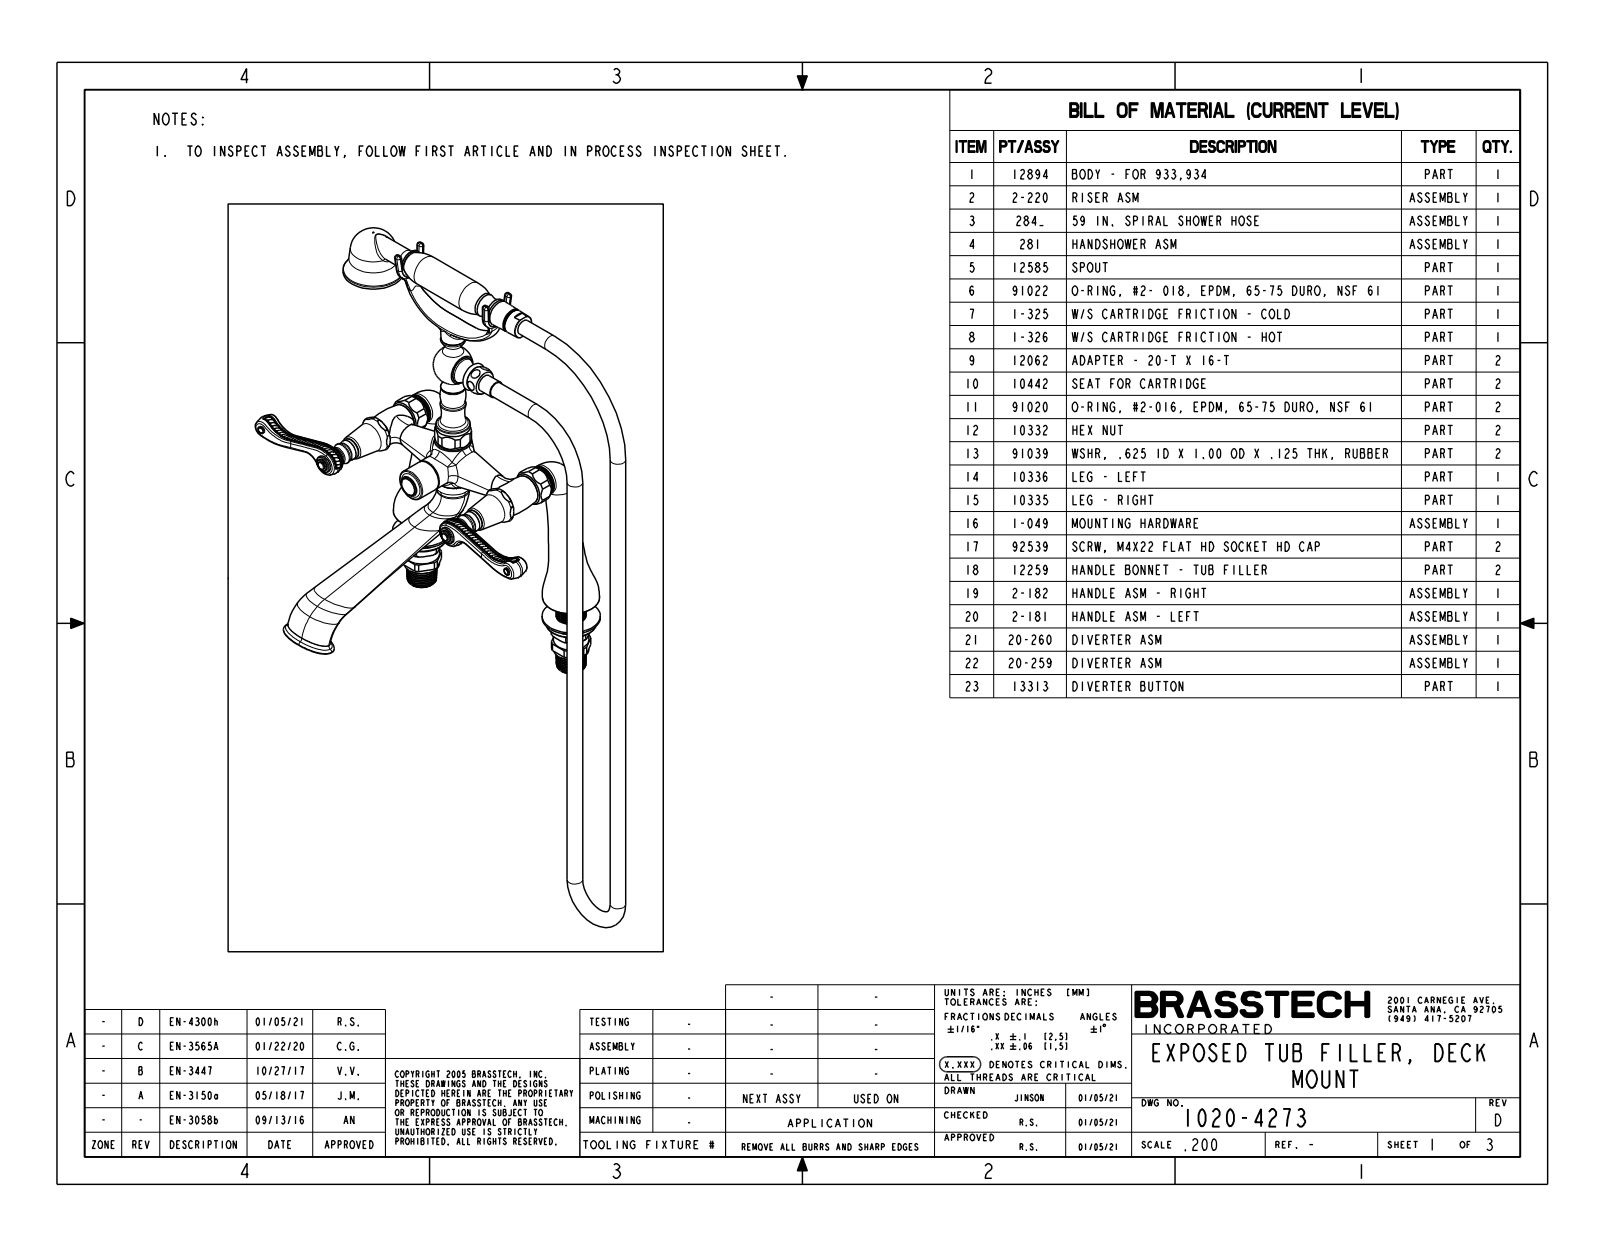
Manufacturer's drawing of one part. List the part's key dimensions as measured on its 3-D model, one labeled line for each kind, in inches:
Part name (STEP PRODUCT): 1020-4273
STEP written by: CREO PARAMETRIC BY PTC INC, 2018400 (CONFIG_CONTROL_DESIGN)
Units: inches
Bodies: 1 solid, 1138 faces (162 planar, 253 cylindrical, 723 other)
Overall size (bounding box): 23.86 × 14.621 × 10.575
Volume: 61.71 in³ · Surface area: 301.1 in²
Round holes (diameter × count): ⌀0.046 ×52
Round bosses / shafts (diameter × count): ⌀0.82 ×4, ⌀0.54 ×4, ⌀0.26 ×4, ⌀0.6 ×3, ⌀1.02 ×2, ⌀0.73 ×2, ⌀0.7 ×2, ⌀0.44 ×2
Partial cylindrical surfaces — rounded edges, fillets, slot ends (radius × count): R0.085 ×32, R11 ×4, R0.637 ×3, R0.595 ×2, R0.405 ×1, R0.406 ×1, R0.45 ×1
Main face-to-face distances: 1.188, 0.983, 0.982, 3, 3.886, 4.188, 1.812, 0.8, 11.041, 11.04
Hole centre spacings: 0.187, 0.367, 0.535, 0.813, 1.021, 0.184, 0.601, 0.685
